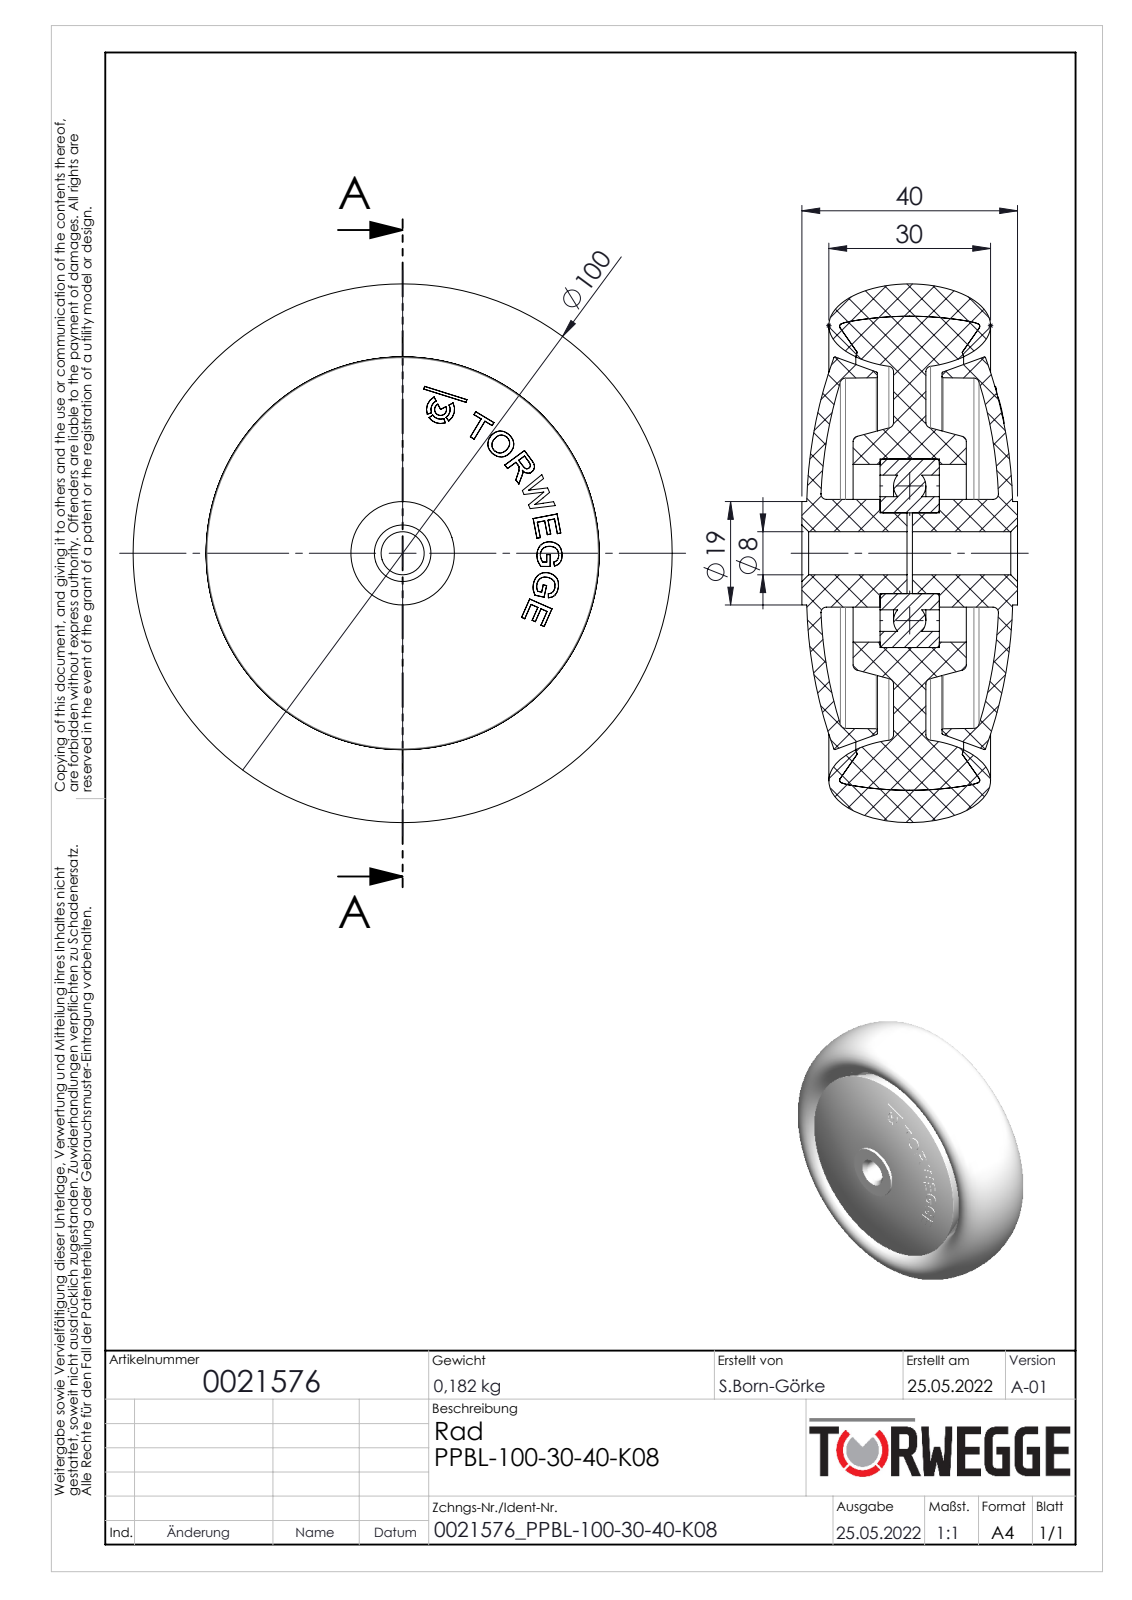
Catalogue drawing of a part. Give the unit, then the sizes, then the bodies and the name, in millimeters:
Units: millimetres
Overall size (bounding box): 100 × 99.69 × 40
Round holes (diameter × count): ⌀8 ×1, ⌀29 ×1, ⌀33 ×1, ⌀35 ×1
Round bosses / shafts (diameter × count): ⌀21 ×1, ⌀20 ×1, ⌀19.2 ×1, ⌀15 ×1
Main face-to-face distances: 6, 2.5, 5, 8.5, 7.5, 13.5, 16, 11, 21, 9.5
Volume: 165 828 mm³ · Surface area: 56 923 mm²
Bodies: 4 solids, 456 faces (20 planar, 34 cylindrical, 402 other)
Part name (STEP PRODUCT): 0021576
STEP written by: SolidWorks 2018 (AUTOMOTIVE_DESIGN)
